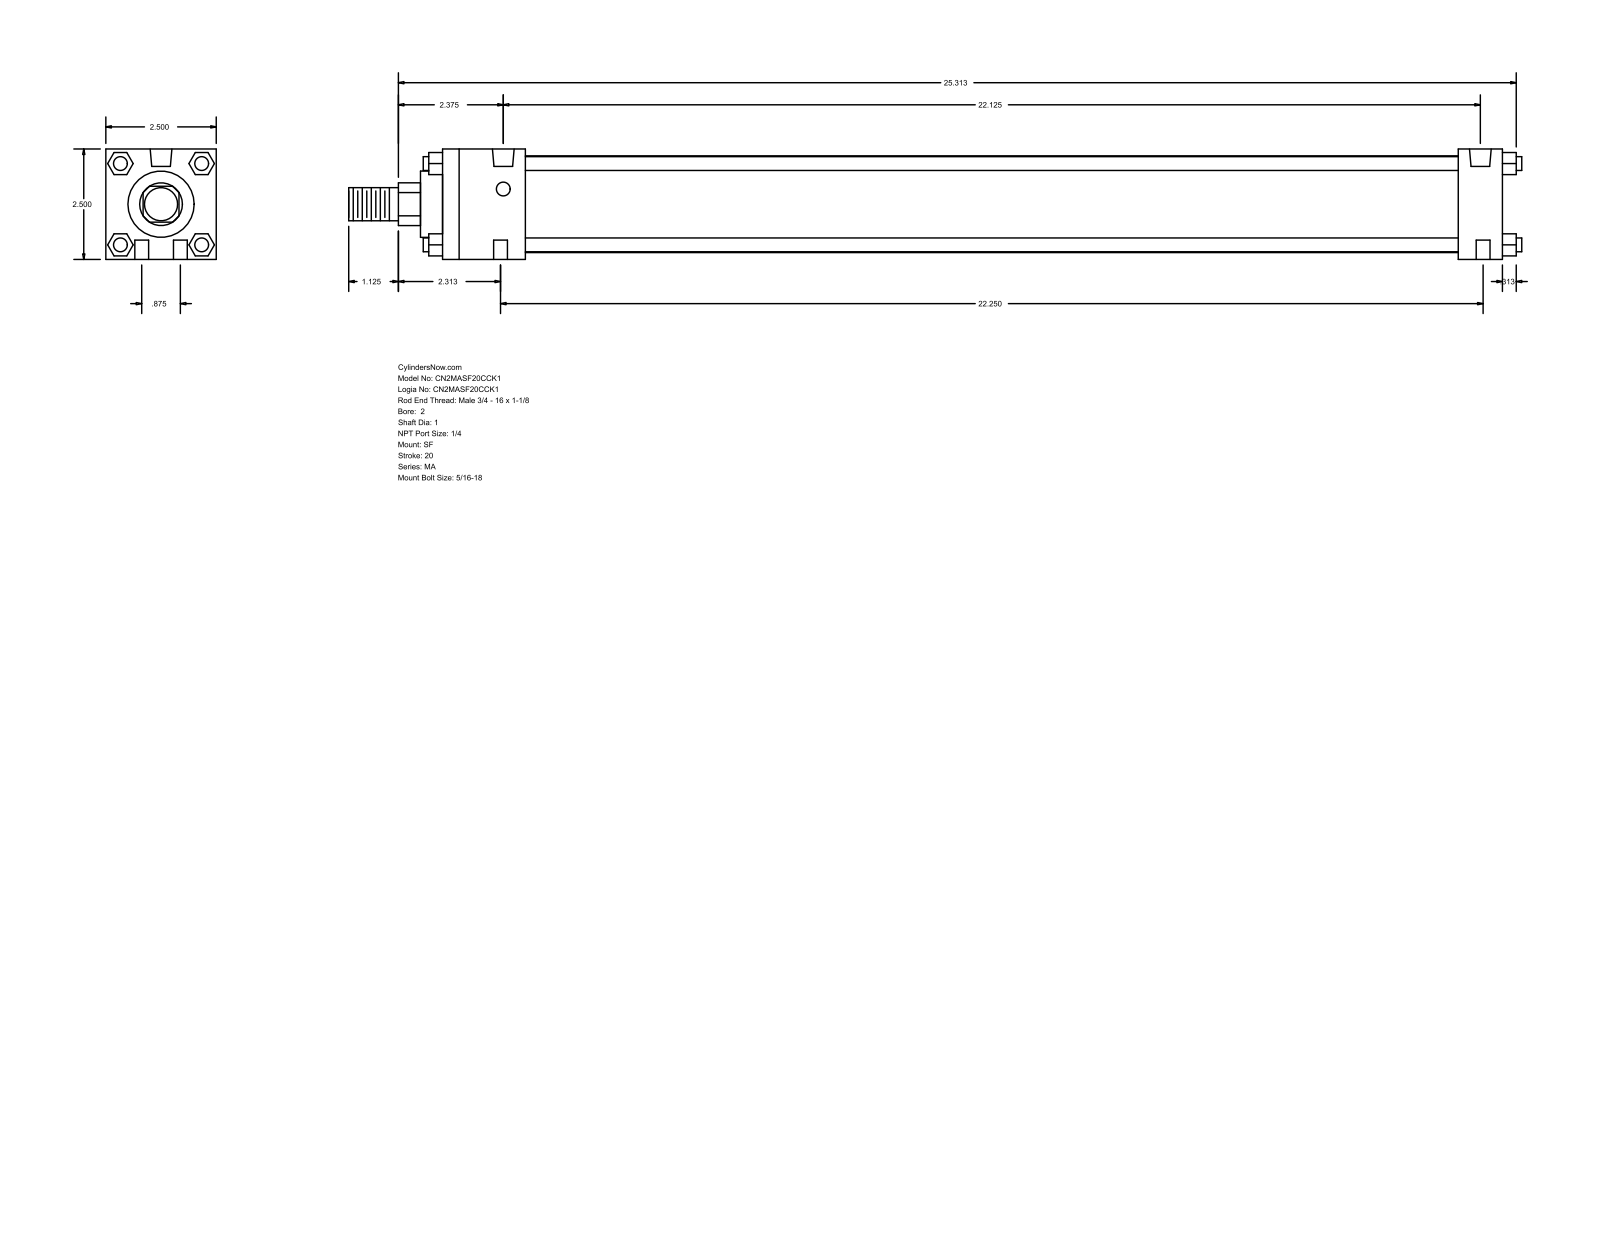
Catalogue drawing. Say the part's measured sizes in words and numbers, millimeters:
The part is named "MA_SF__0200_1". Its 3-D file was written by "GSSL Pune (CONFIG_CONTROL_DESIGN)". It is 0 solids with 124 faces: 94 planar, 30 cylindrical and 0 other. Overall it measures 674.69 by 63.5 by 63.5 millimeters. Round holes: 6 of diameter 7.94, 2 of diameter 12.49. Round bosses or shafts: 4 of diameter 7.94, 1 of diameter 55.63, 1 of diameter 38.1, 1 of diameter 25.4, 1 of diameter 19.05. Partial cylindrical surfaces (rounded edges, fillets, slot ends): 1 of radius 12.29. The main face-to-face distances are 63.5, 609.6, 12.7, 25.4, 584.2, 47.63, 536.57, 561.97, 40.47, 23.37. The hole center spacings are 11.22, 563.67, 22.22, 561.97, 565.15, 565.59.
